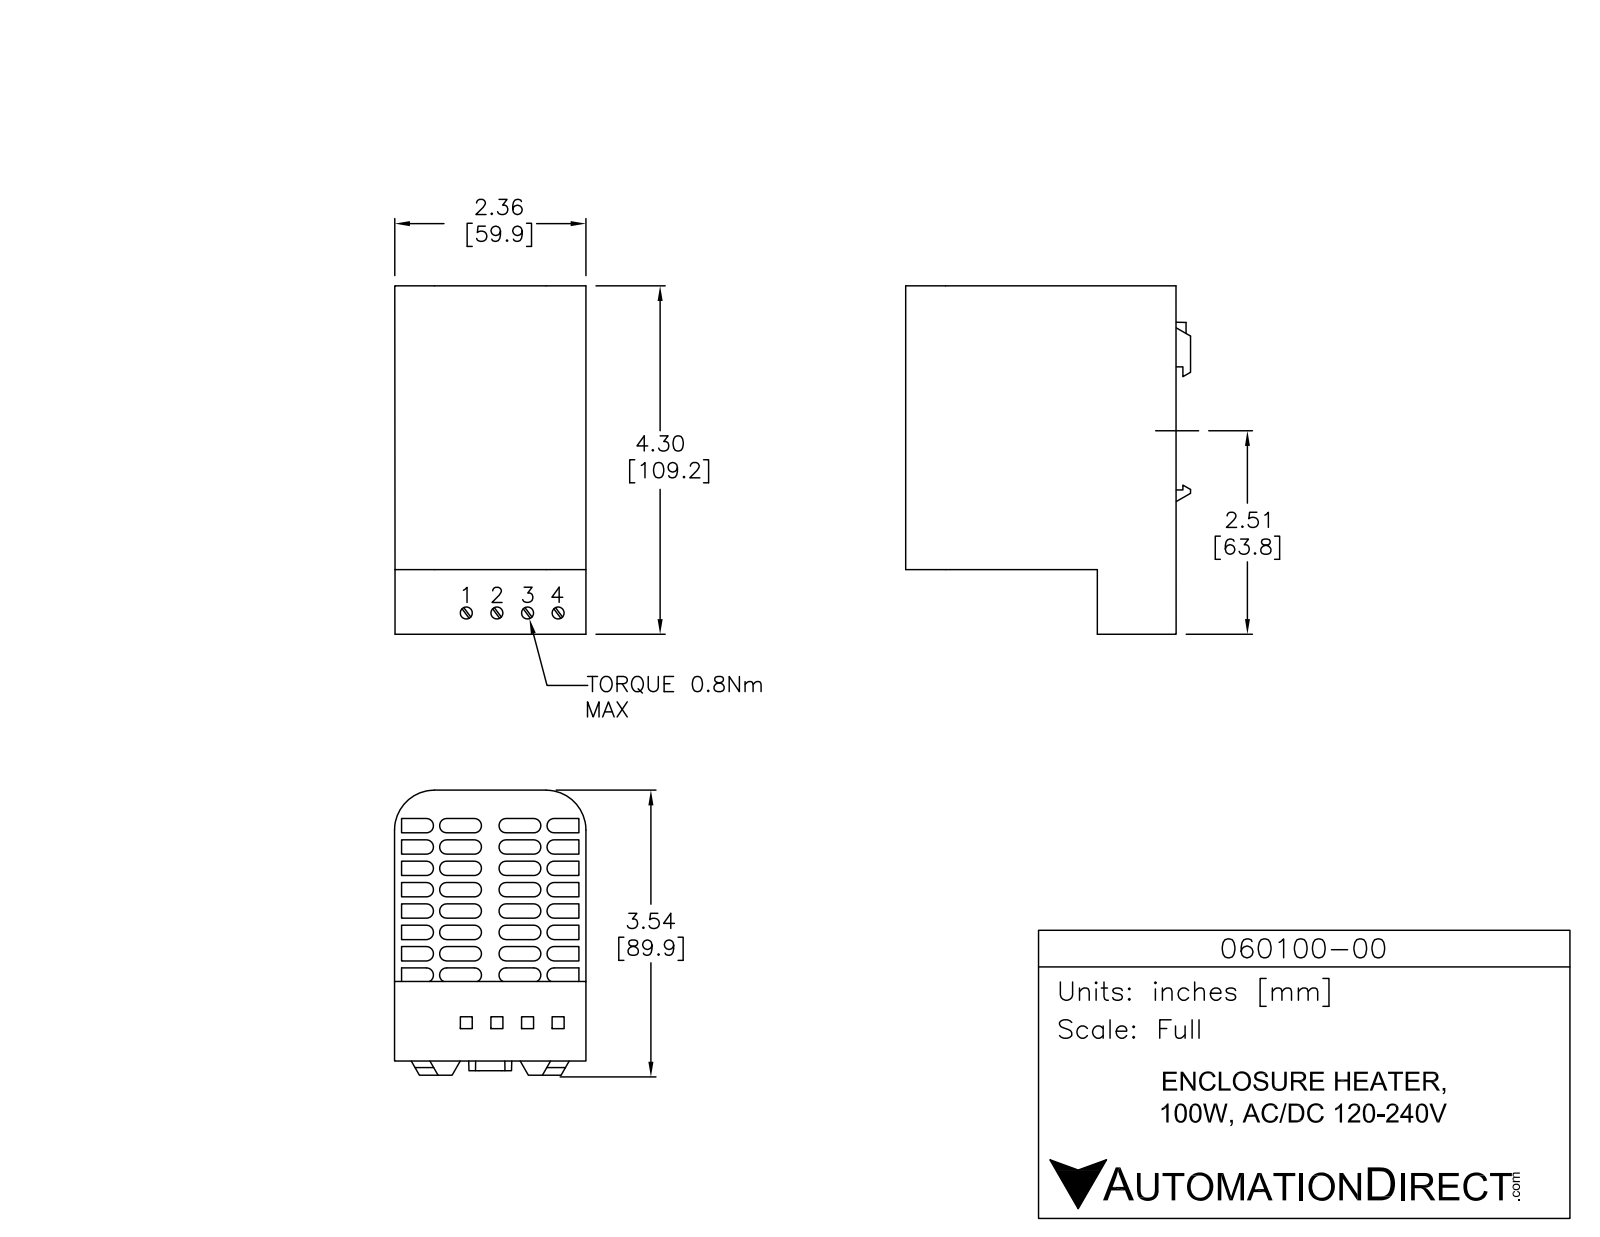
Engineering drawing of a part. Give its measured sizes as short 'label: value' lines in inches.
name: 060100-00
written by: SolidWorks 2013 (AUTOMOTIVE_DESIGN)
unit: in
bodies: 1 solid, 817 faces (601 planar, 210 cylindrical, 6 other)
size: 4.345 × 3.58 × 2.35
volume: 26.66 in³; area: 90.82 in²
holes: 3× ⌀0.185, 1× ⌀0.185
rounds: 88× R0.07, 18× R0.035, 6× R0.06, 2× R0.8
face distances: 0.03, 0.215, 0.061, 2.336, 0.2, 3.18, 2.306, 0.43, 0.03, 0.091
hole spacings: 0.4, 0.8, 1.2
